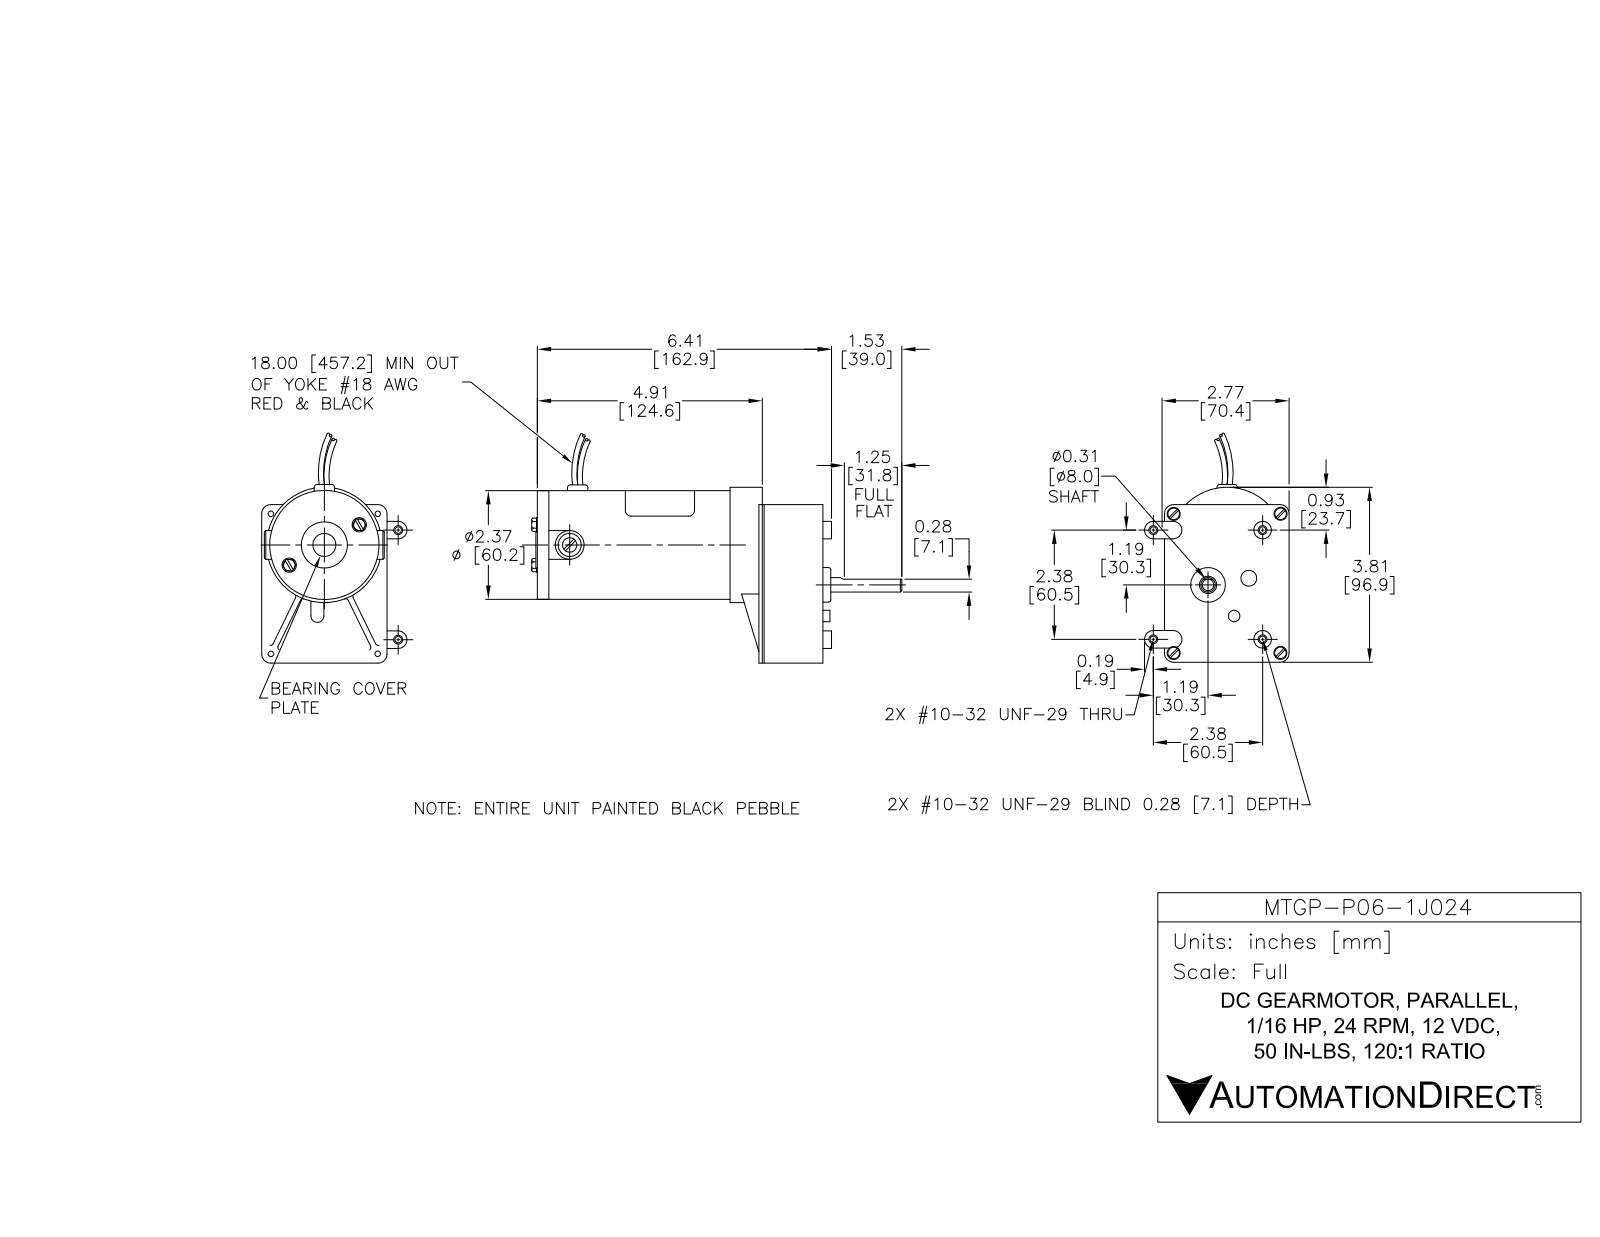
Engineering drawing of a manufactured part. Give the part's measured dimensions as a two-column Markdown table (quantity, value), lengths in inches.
| quantity | value |
| --- | --- |
| part name | MTGP-P06-1J024 |
| STEP written by | SolidWorks 2016 (AUTOMOTIVE_DESIGN) |
| units | inches |
| bodies | 27 solids, 266 faces (115 planar, 130 cylindrical, 21 other) |
| overall size | 7.922 × 5.092 × 3.181 |
| volume | 20.18 in³ |
| surface area | 156.4 in² |
| round holes (diameter × count) | 0.194 × 5, 0.063 × 4, 0.283 × 4, 0.156 × 2, 0.25 × 1, 0.312 × 1, 0.562 × 1, 1 × 1, 2.25 × 1 |
| round bosses / shafts (diameter × count) | 0.312 × 4, 0.38 × 2, 0.1 × 2, 2.46 × 1, 2.375 × 1, 0.75 × 1, 0.625 × 1, 0.625 × 1 |
| partial cylindrical surfaces (radius × count) | 0.031 × 10, 0.1 × 4, 0.19 × 4, 0.25 × 2, 0.134 × 1, 0.141 × 1, 1.222 × 1 |
| main face-to-face distances | 1.4, 0.25, 4.833, 6.233, 4.583, 5.983, 4.194, 3.944, 0.639, 2.039 |
| hole center spacings | 1.223, 1.729, 0.373, 0.44, 0.875, 1.306, 1.332, 1.539 |
